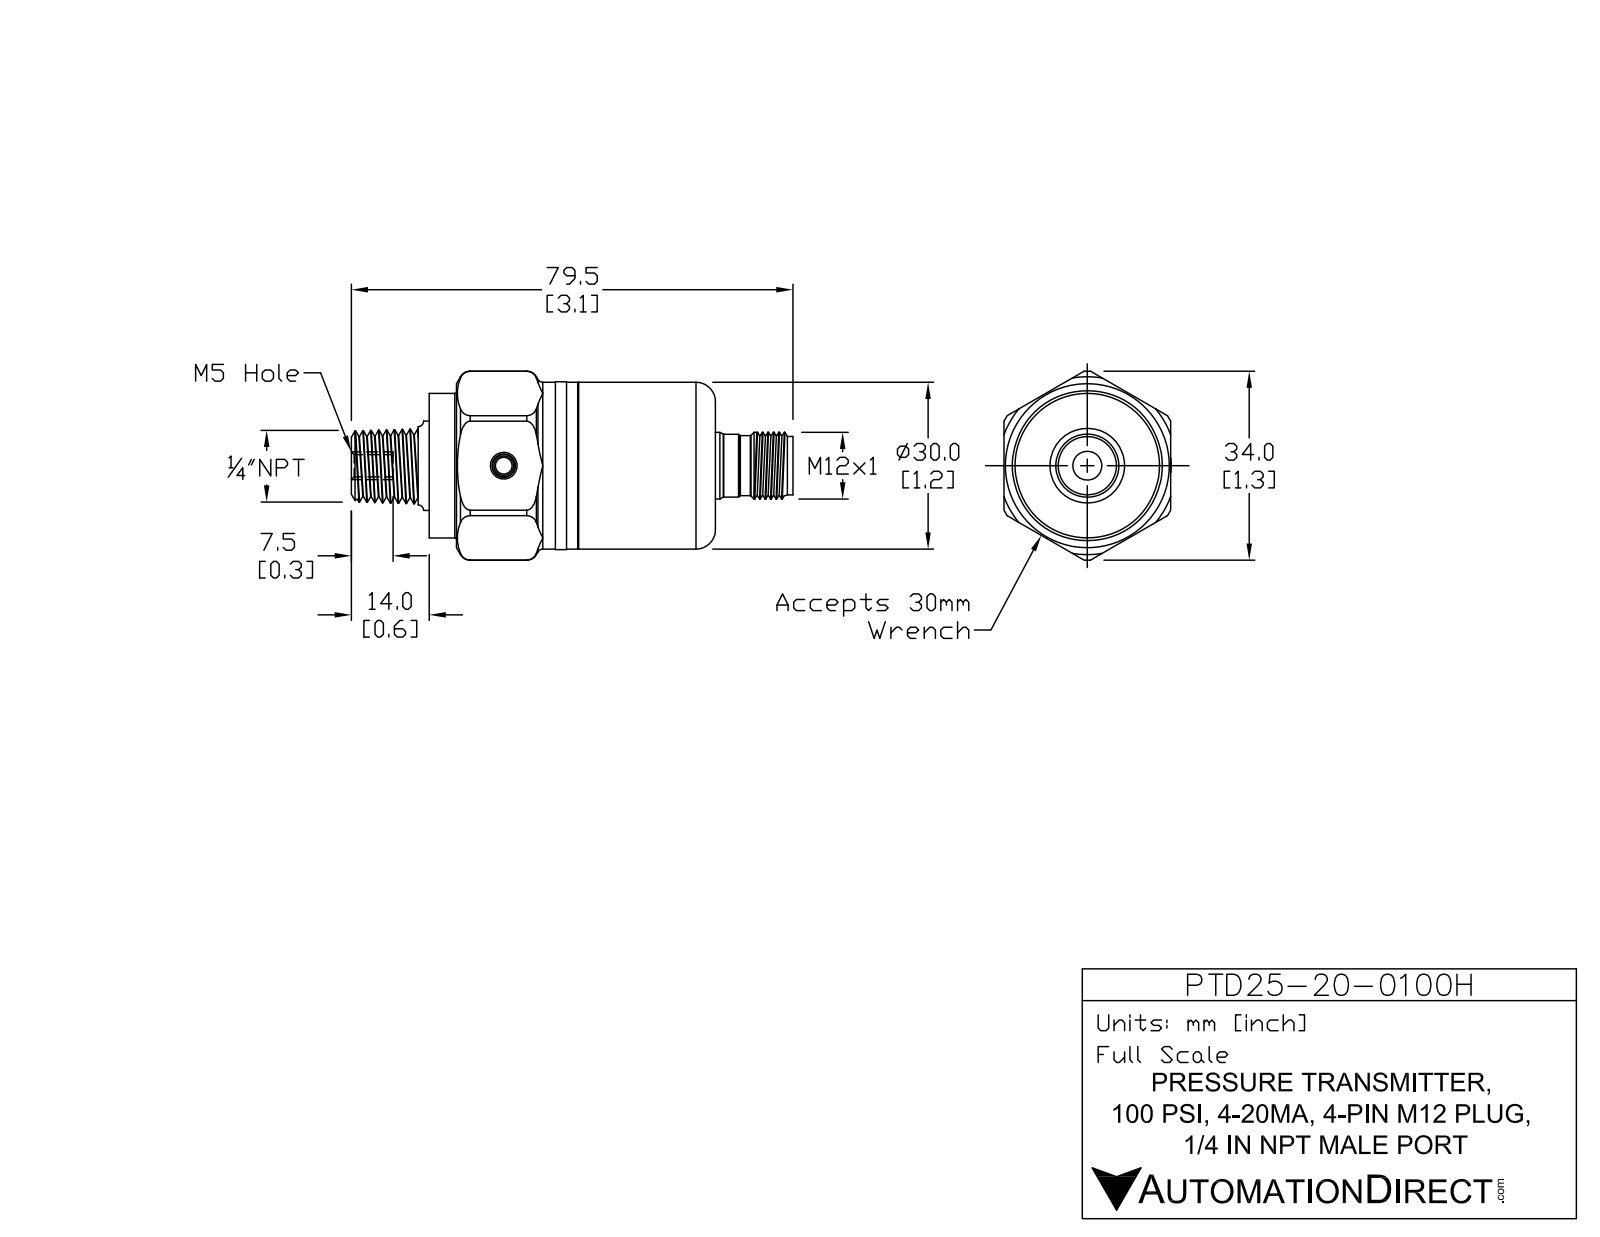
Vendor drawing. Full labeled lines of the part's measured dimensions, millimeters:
Part name (STEP PRODUCT): PTD25-20-0100H
STEP written by: SolidWorks 2017 (AUTOMOTIVE_DESIGN)
Units: millimetres
Bodies: 1 solid, 124 faces (36 planar, 59 cylindrical, 29 other)
Overall size (bounding box): 79.5 × 33.78 × 31.7
Volume: 39 212 mm³ · Surface area: 8 088 mm²
Round holes (diameter × count): ⌀4 ×1, ⌀8.5 ×1
Round bosses / shafts (diameter × count): ⌀30.05 ×1, ⌀30 ×1, ⌀25.96 ×1, ⌀14 ×1, ⌀13.5 ×1, ⌀12 ×1
Partial cylindrical surfaces — rounded edges, fillets, slot ends (radius × count): R3.76 ×1, R16.95 ×1
Main face-to-face distances: 51, 29.98, 30, 48, 3, 65, 17, 14, 30.01, 5.65
